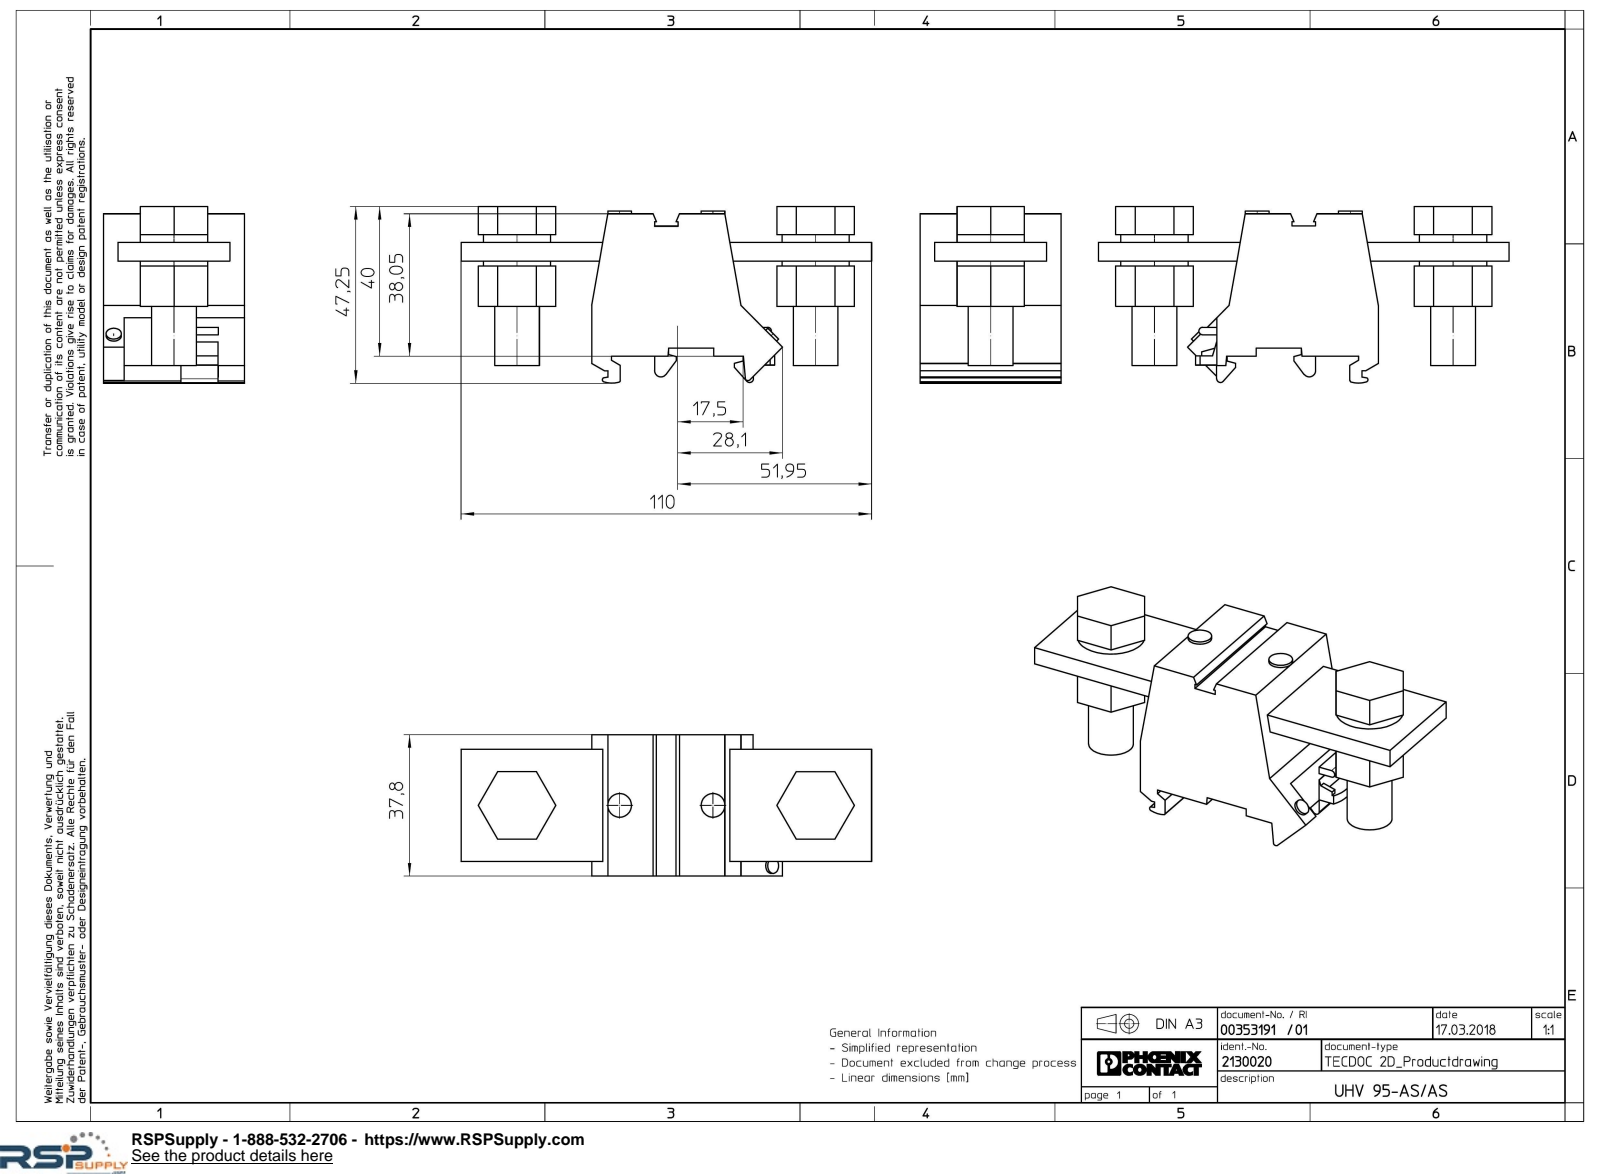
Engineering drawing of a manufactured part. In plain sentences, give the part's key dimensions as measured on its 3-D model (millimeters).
The part is named "UHV_95_AS_AS-select". Its 3-D file was written by "Creo Elements/Direct Modeling 18.1I 14-Aug-2016 (C) Parametric Technology GmbH (AUTOMOTIVE_DESIGN)". It is 1 solid with 155 faces: 128 planar, 27 cylindrical and 0 other. Overall it measures 110 by 47.25 by 37.8 millimeters. Its volume is 82 801 cubic millimeters and its surface area 20 108 square millimeters. Round bosses or shafts: 2 of diameter 18, 2 of diameter 12, 2 of diameter 6.35, 1 of diameter 4.11. Partial cylindrical surfaces (rounded edges, fillets, slot ends): 3 of radius 0.5, 2 of radius 1, 1 of radius 0.63, 1 of radius 1.7, 1 of radius 7.2, 1 of radius 11. The main face-to-face distances are 5, 37.8, 18, 7.65, 27.9, 30.4, 38.05, 12.65, 25.4, 24.
